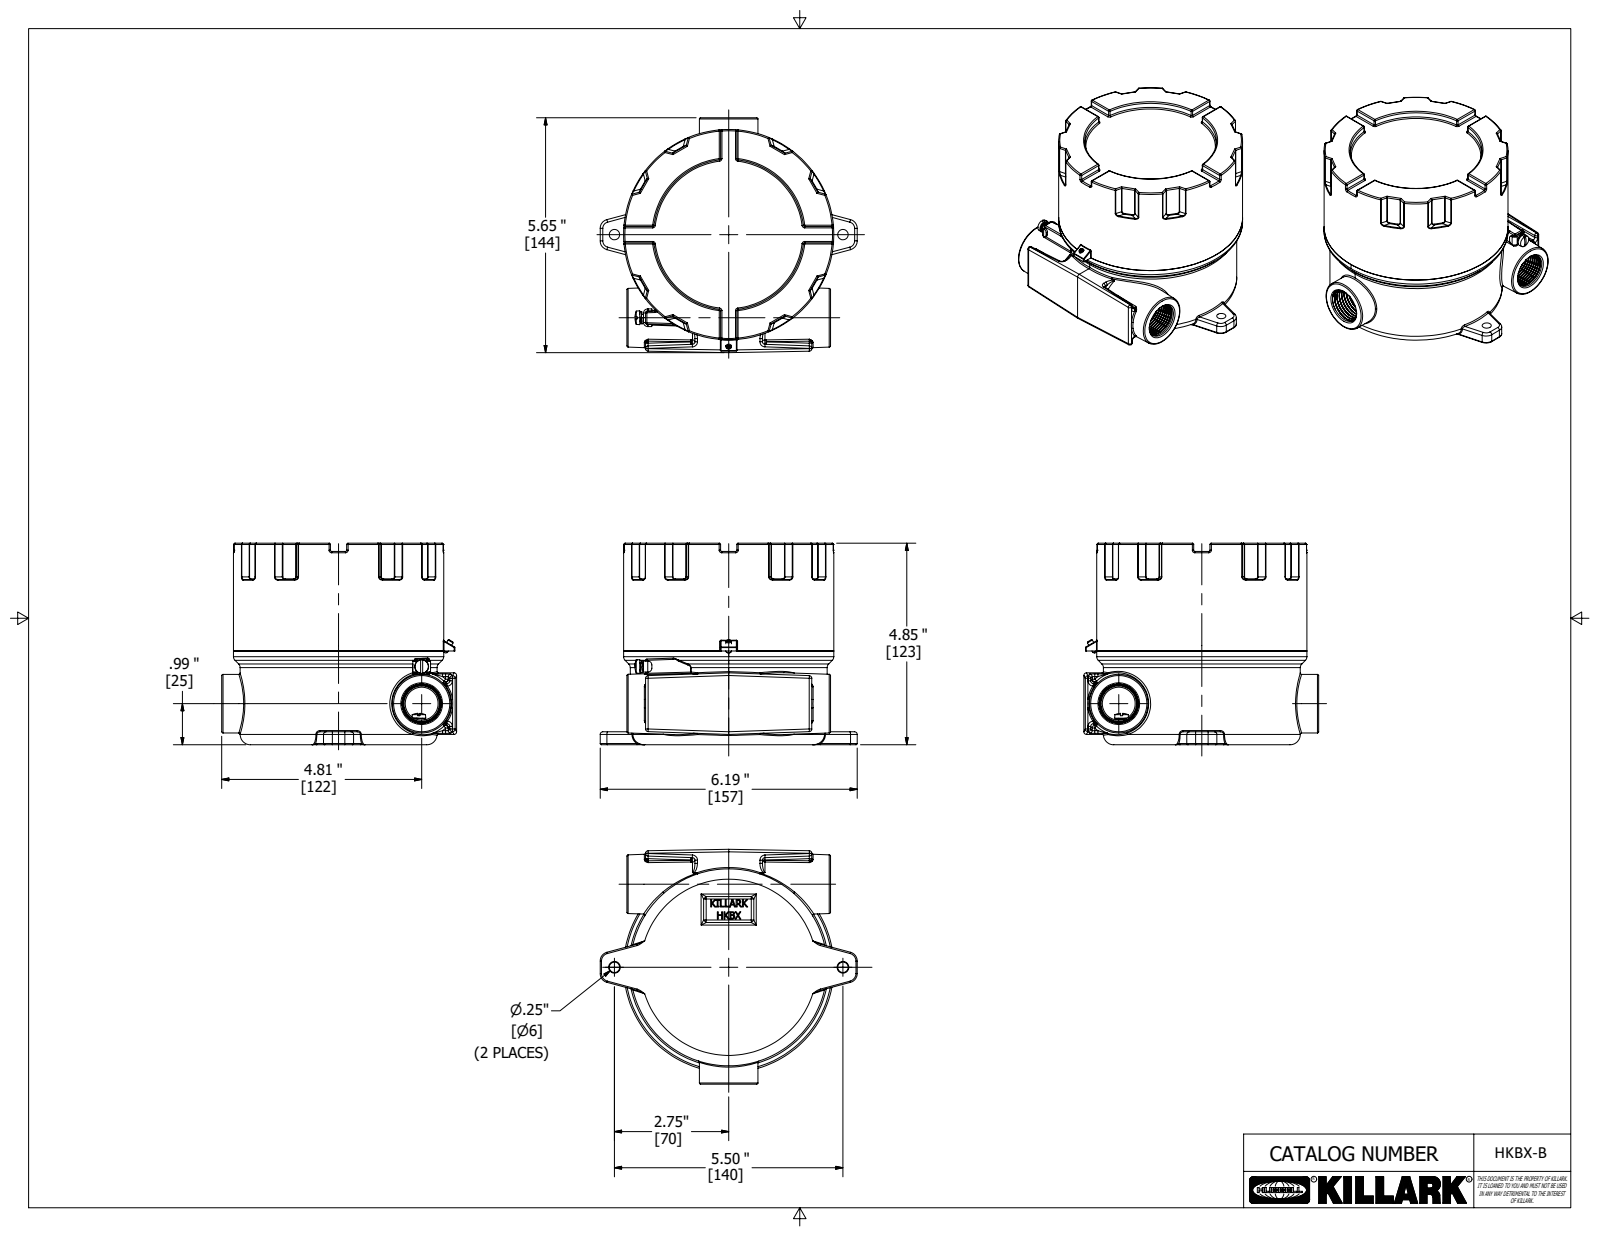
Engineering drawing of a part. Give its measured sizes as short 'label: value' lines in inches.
name: KIL_HKBX-B; 51637ABAM for web; 51641ABAM for web; 51777AAAB (+4 more)
written by: Autodesk Inventor 2020 (AUTOMOTIVE_DESIGN)
unit: in
bodies: 13 solids, 972 faces (321 planar, 247 cylindrical, 404 other)
size: 24.949 × 14.924 × 4.852
volume: 36.52 in³; area: 587 in²
holes: 2× ⌀0.13, 2× ⌀0.18, 2× ⌀0.25, 1× ⌀0.104, 1× ⌀0.792, 1× ⌀3.624, 1× ⌀4.2, 1× ⌀4.34, 1× ⌀4.39, 1× ⌀4.86
bosses: 2× ⌀0.293, 2× ⌀0.158, 1× ⌀5.06, 1× ⌀4.74, 1× ⌀4.724, 1× ⌀4.585, 1× ⌀1.41, 1× ⌀0.138
rounds: 61× R0.031, 51× R0.062, 47× R0.016, 8× R0.125, 4× R0.05, 4× R0.094, 4× R0.1, 4× R0.219
face distances: 0.25, 4.402, 4.152, 4.652, 0.45, 0.2, 4.852, 4.602, 0.5, 3.902
hole spacings: 2.75, 3.361, 0.892, 1.932, 5.5
